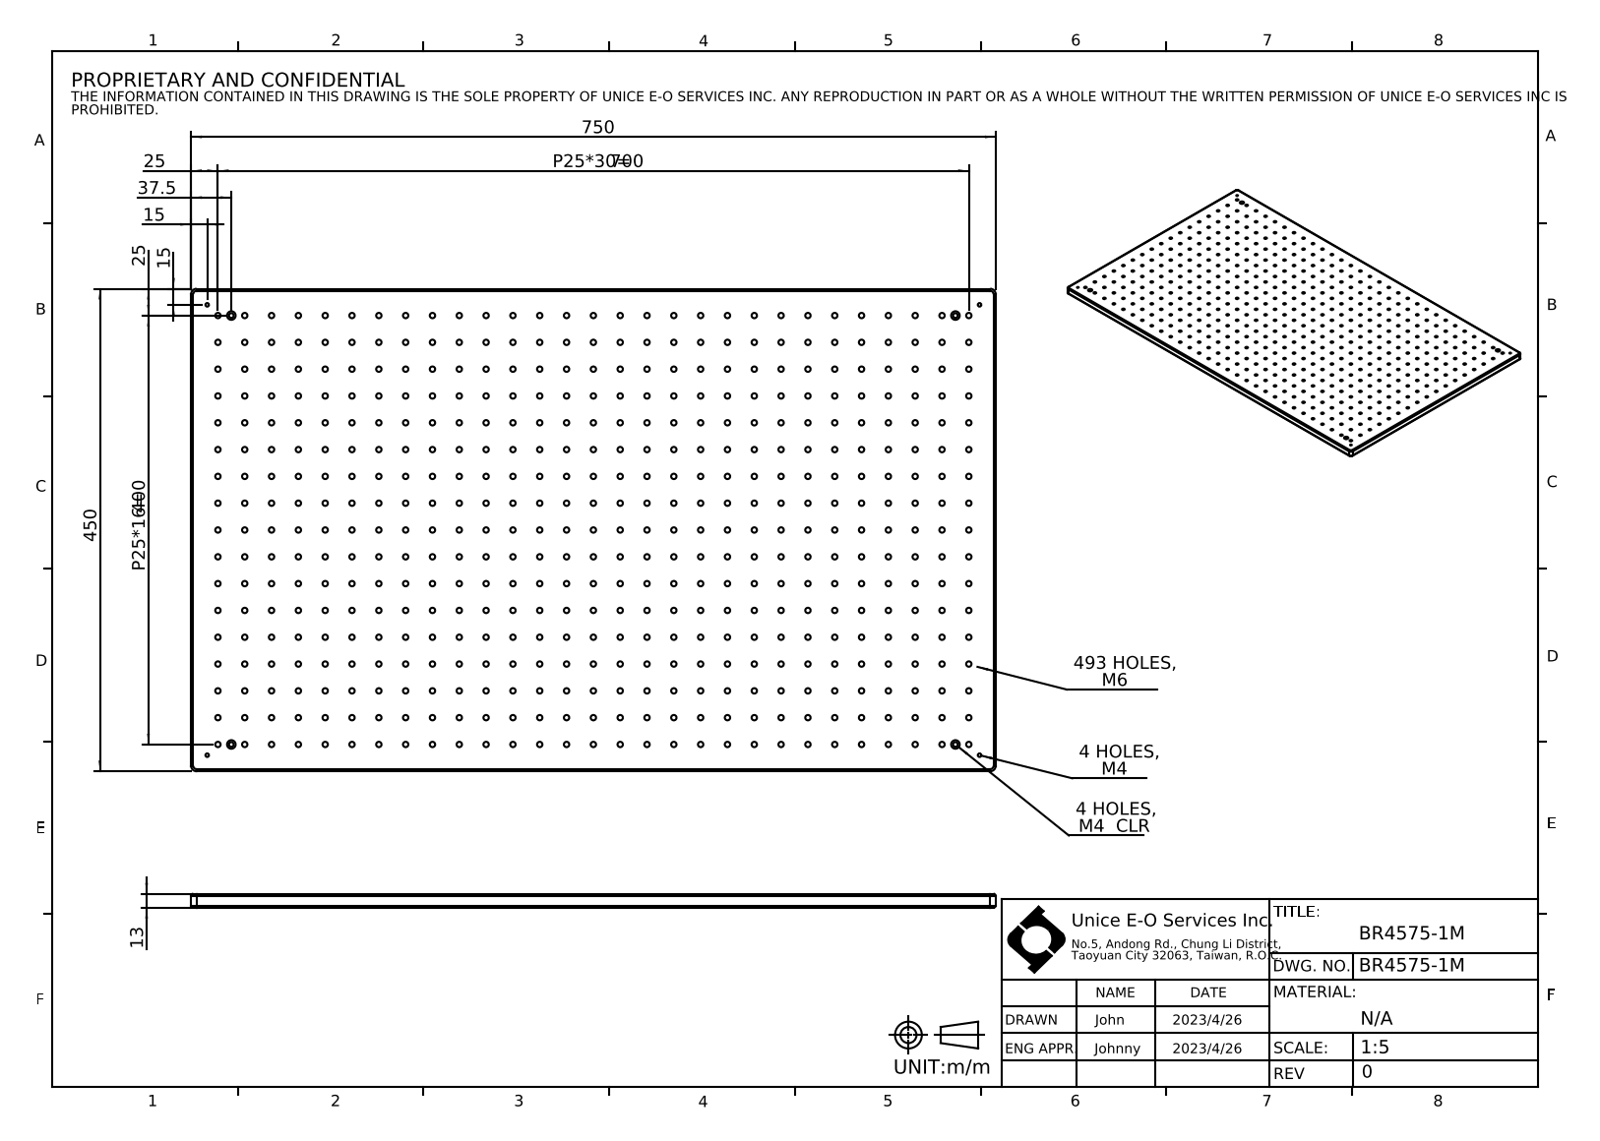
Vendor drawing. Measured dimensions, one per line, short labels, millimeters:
name: BR4575-1M
written by: SolidWorks 2022 (CONFIG_CONTROL_DESIGN)
unit: mm
bodies: 1 solid, 1040 faces (10 planar, 1022 cylindrical, 8 other)
size: 750 × 450 × 13
volume: 4 255 000 mm³; area: 784 521 mm²
holes: 493× ⌀5, 4× ⌀3.3, 4× ⌀4.5, 4× ⌀8
rounds: 8× R2, 4× R5
face distances: 13, 450, 750, 8.6, 4.4
hole spacings: 25, 50, 75, 100, 125, 150, 175, 200
